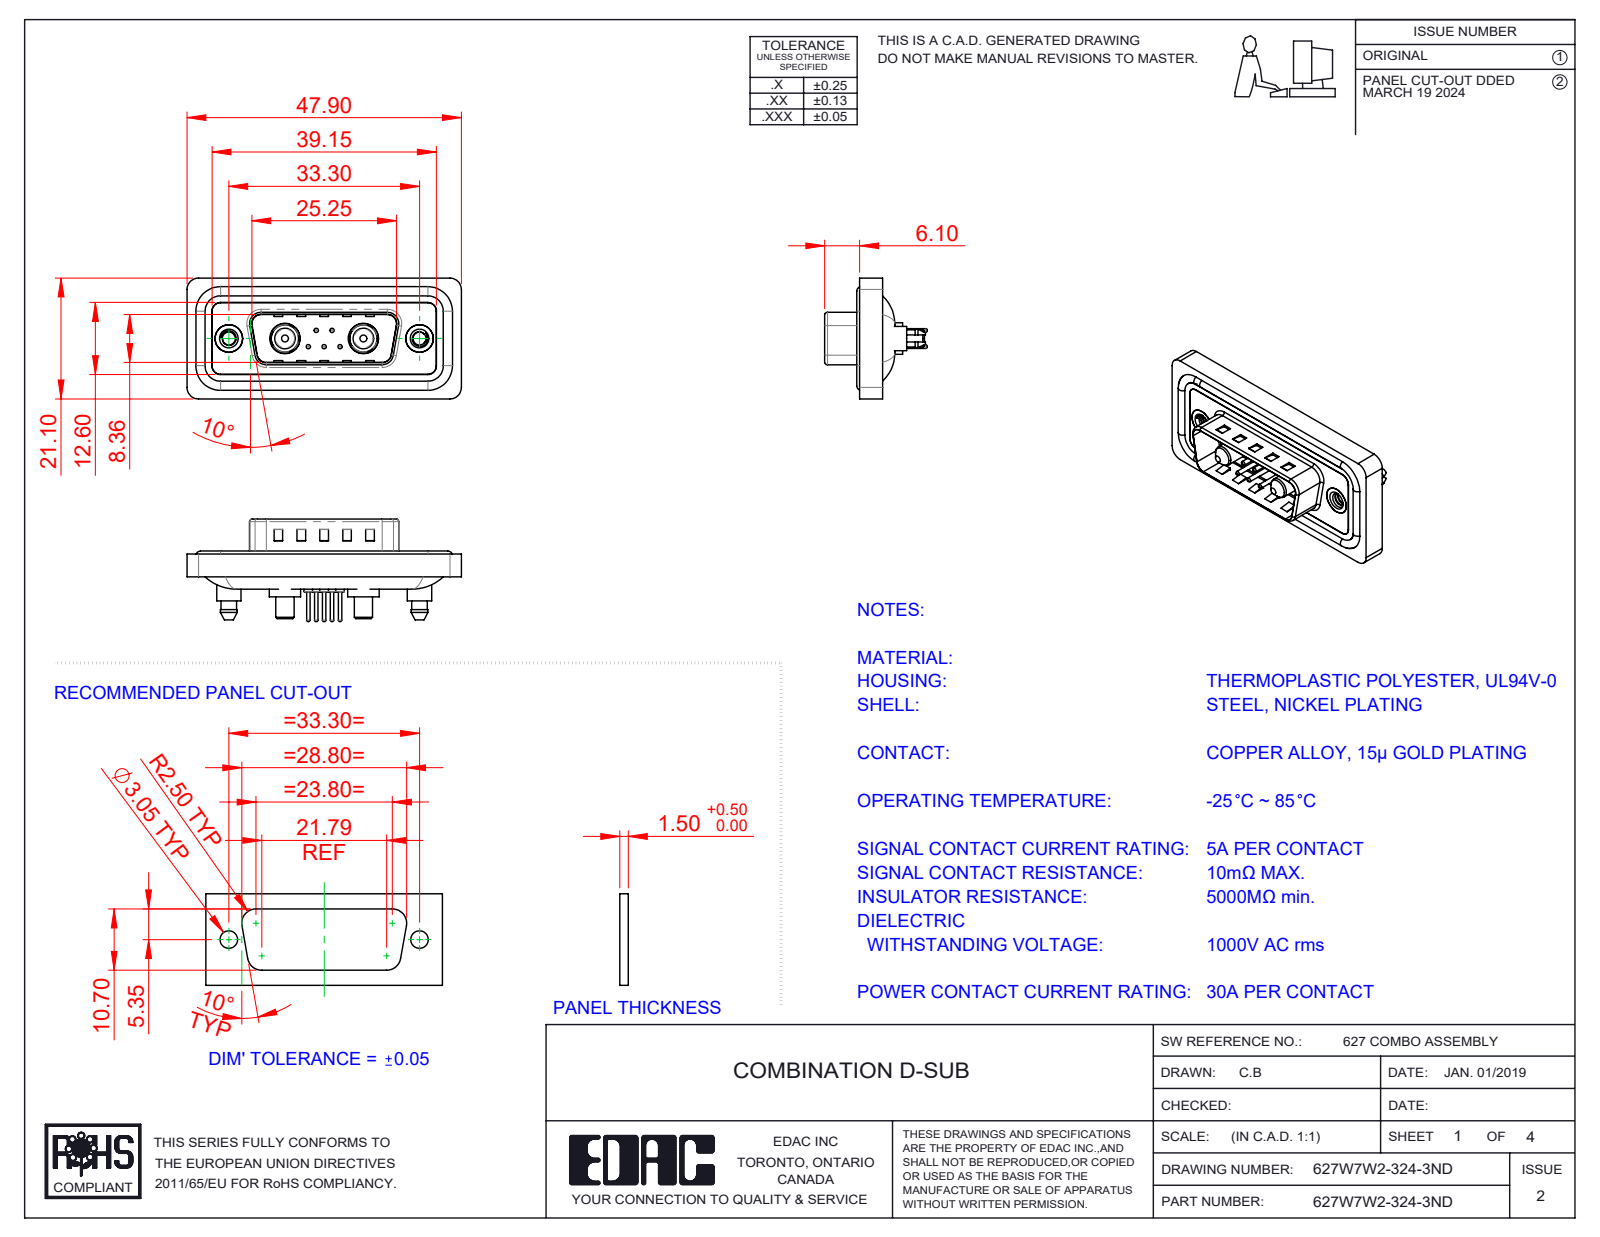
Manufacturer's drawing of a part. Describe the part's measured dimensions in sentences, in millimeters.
The part is named "627Combo Threaded Boardlock_5; 627Combo Contact Row 2_24; 627Combo Shell Rear_15 Contacts; 627Combo Threaded Boardlock_D (+6 more)". Its 3-D file was written by "SolidWorks 2023 (CONFIG_CONTROL_DESIGN)". It is 16 solids with 768 faces: 248 planar, 332 cylindrical and 188 other. Overall it measures 47.9 by 21.1 by 17.9 millimeters. Its volume is 5 666 cubic millimeters and its surface area 9 138 square millimeters. Round holes: 5 of diameter 0.75, 5 of diameter 1.6, 5 of diameter 2, 2 of diameter 2.26, 2 of diameter 4, 2 of diameter 4.8, 2 of diameter 4.85, 2 of diameter 5, 2 of diameter 5.3. Round bosses or shafts: 5 of diameter 1.5, 5 of diameter 0.6, 4 of diameter 1.6, 2 of diameter 5.5, 2 of diameter 5.4, 2 of diameter 5.2, 2 of diameter 4.9, 2 of diameter 4.75. Partial cylindrical surfaces (rounded edges, fillets, slot ends): 28 of radius 1.5, 20 of radius 2, 10 of radius 1.6, 8 of radius 0.5, 4 of radius 0.25, 4 of radius 0.6, 4 of radius 0.65, 4 of radius 0.9. The main face-to-face distances are 0.4, 1.1, 1.5, 1.6, 0.5, 3.1, 2.9, 0.7, 4, 0.82. The hole center spacings are 3.16, 2.77, 9.8, 23.5, 4.31, 4.33, 5.03, 5.04.
